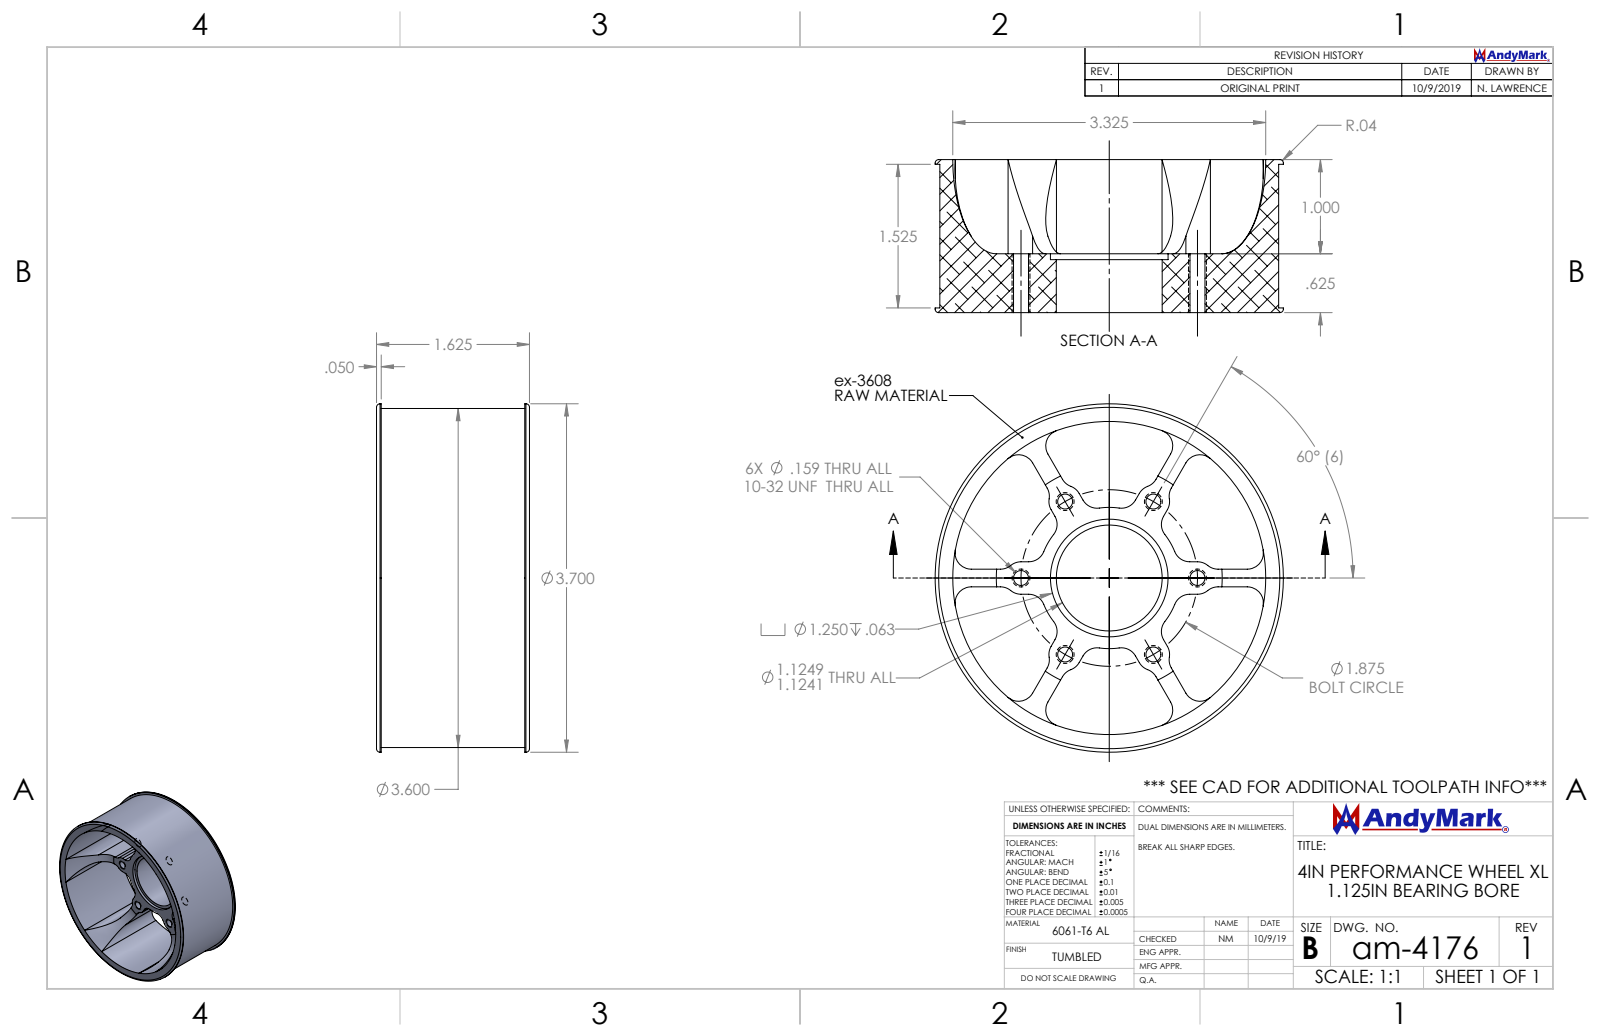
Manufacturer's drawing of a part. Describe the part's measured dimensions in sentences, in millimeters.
The part is named "am-4176 4IN Extrusion Performance Wheel 1.5IN Wide 1125 Bearing". Its 3-D file was written by "SolidWorks 2019 (AUTOMOTIVE_DESIGN)". It is 1 solid with 109 faces: 30 planar, 71 cylindrical and 8 other. Overall it measures 94 by 94 by 41.3 millimeters. Its volume is 64 930 cubic millimeters and its surface area 36 040 square millimeters. Round holes: 6 of diameter 4, 1 of diameter 28.6, 1 of diameter 31.8. Round bosses or shafts: 1 of diameter 94, 1 of diameter 91.4. Partial cylindrical surfaces (rounded edges, fillets, slot ends): 42 of radius 4.4, 1 of radius 19.1, 1 of radius 42.2, 1 of radius 42.2. The main face-to-face distances are 41.3, 4.7, 15.9, 25.4, 1.3, 40, 14.6, 38.7, 24.1, 2. The hole center spacings are 23.8, 41.2, 47.6, 23.8.
